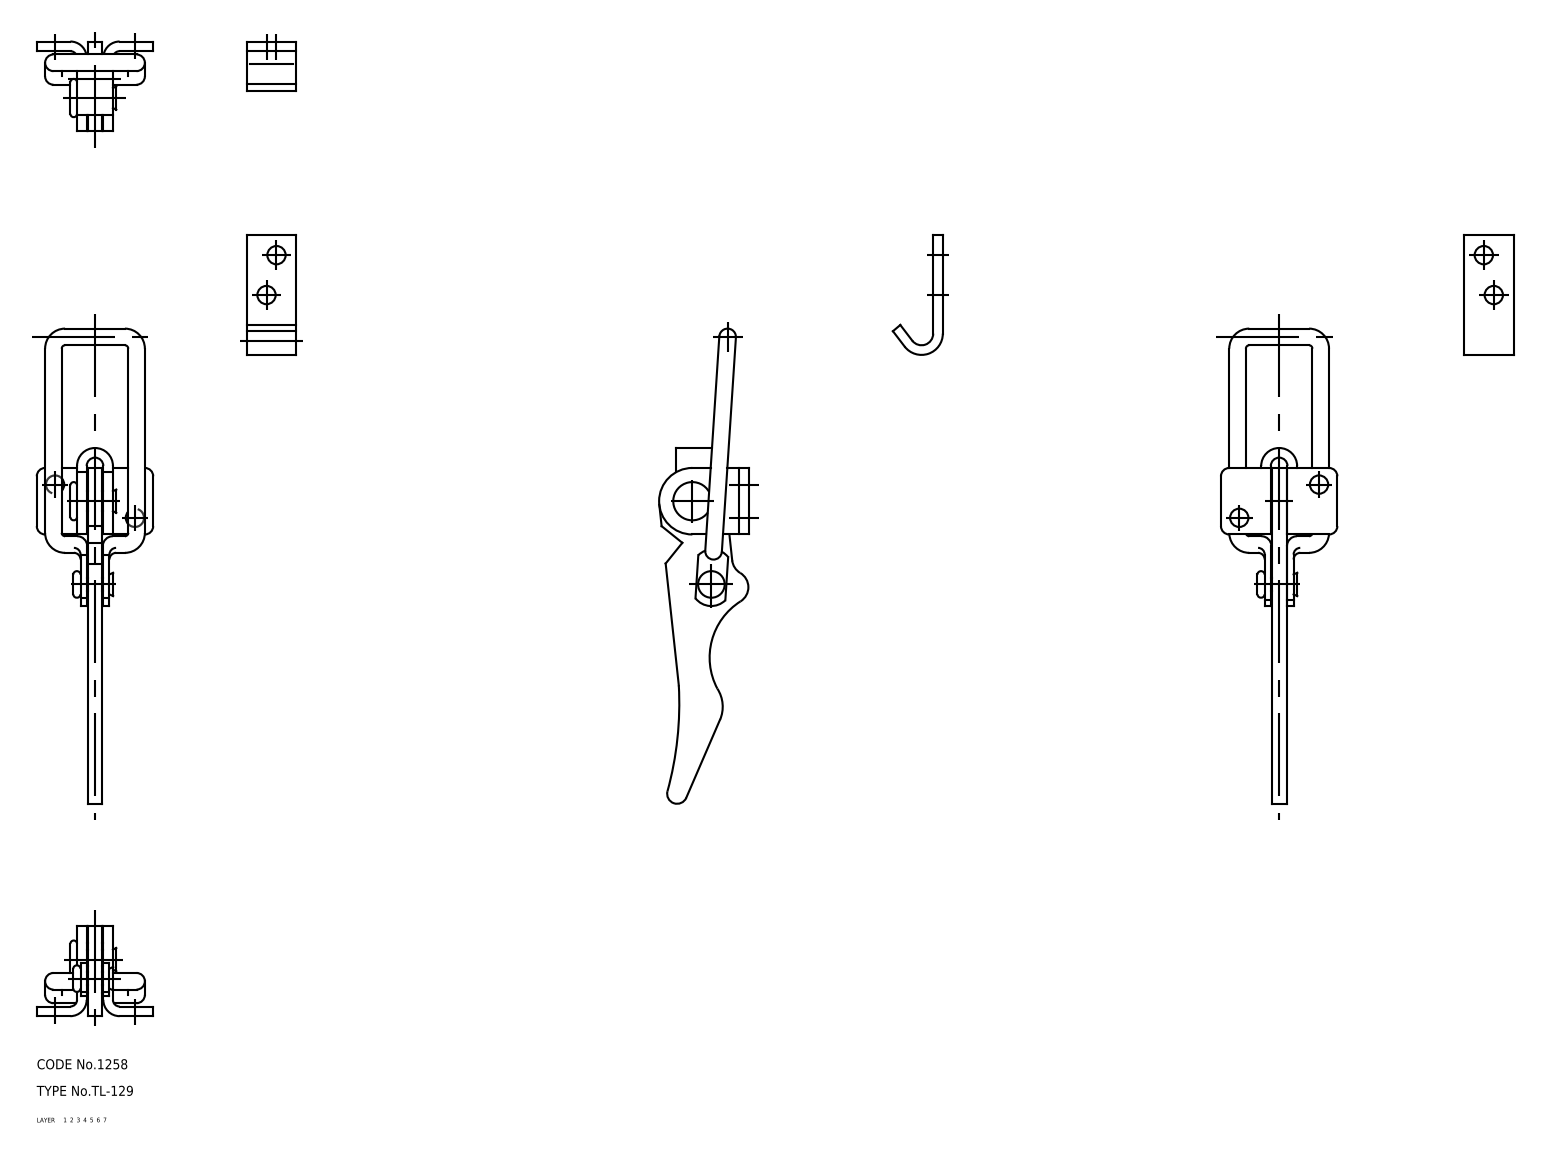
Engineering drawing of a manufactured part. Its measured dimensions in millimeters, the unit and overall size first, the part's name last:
Units: millimetres
Overall size (bounding box): 171 × 35 × 27
Volume: 17 260 mm³ · Surface area: 13 799 mm²
Bodies: 6 solids, 132 faces (0 planar, 0 cylindrical, 132 other)
Part name (STEP PRODUCT): rivet_2; rivet_1; lever; keeper (+3 more)
STEP written by: CADfix (AUTOMOTIVE_DESIGN)
